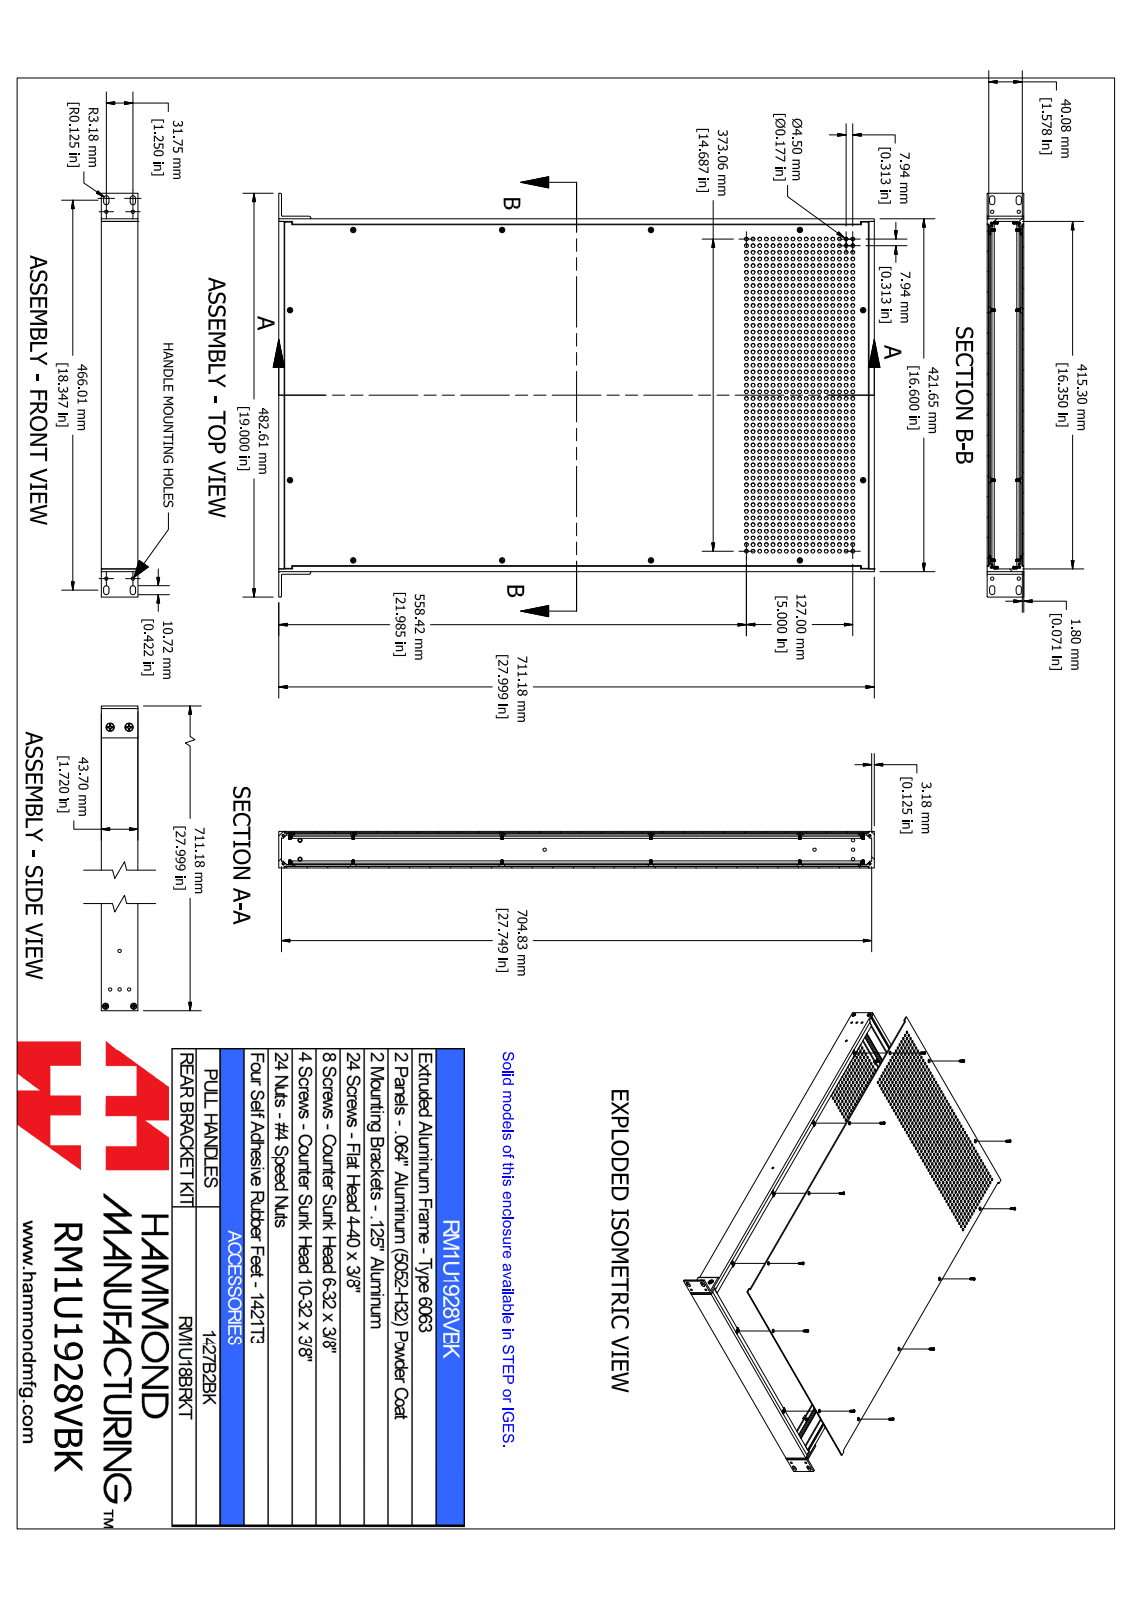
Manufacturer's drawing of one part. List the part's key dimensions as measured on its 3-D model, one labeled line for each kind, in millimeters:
Part name (STEP PRODUCT): RM1U1928VBK
STEP written by: SolidWorks 2021 (AUTOMOTIVE_DESIGN)
Units: millimetres
Bodies: 68 solids, 4262 faces (1076 planar, 2254 cylindrical, 932 other)
Overall size (bounding box): 711.2 × 482.6 × 43.7
Volume: 1 495 000 mm³ · Surface area: 1 510 000 mm²
Round holes (diameter × count): ⌀4.5 ×1632, ⌀4 ×17, ⌀4.1 ×16, ⌀4.2 ×8, ⌀4 ×4, ⌀4 ×4, ⌀4.3 ×4, ⌀4 ×3, ⌀5 ×2
Round bosses / shafts (diameter × count): ⌀5.1 ×16, ⌀2.8 ×16, ⌀6 ×4, ⌀3.5 ×4, ⌀9.1 ×2, ⌀4.8 ×2
Partial cylindrical surfaces — rounded edges, fillets, slot ends (radius × count): R0.3 ×96, R0.6 ×96, R0.2 ×48, R0.4 ×48, R0.4 ×16, R1 ×16, R1 ×16, R0.9 ×10
Main face-to-face distances: 1.8, 41.9, 43.7, 40.1, 3.2, 418.5, 2.2, 41.5, 0.4, 39.7
Hole centre spacings: 177.8, 433, 355.6, 531.4, 678.4, 122, 203.2, 270.8
